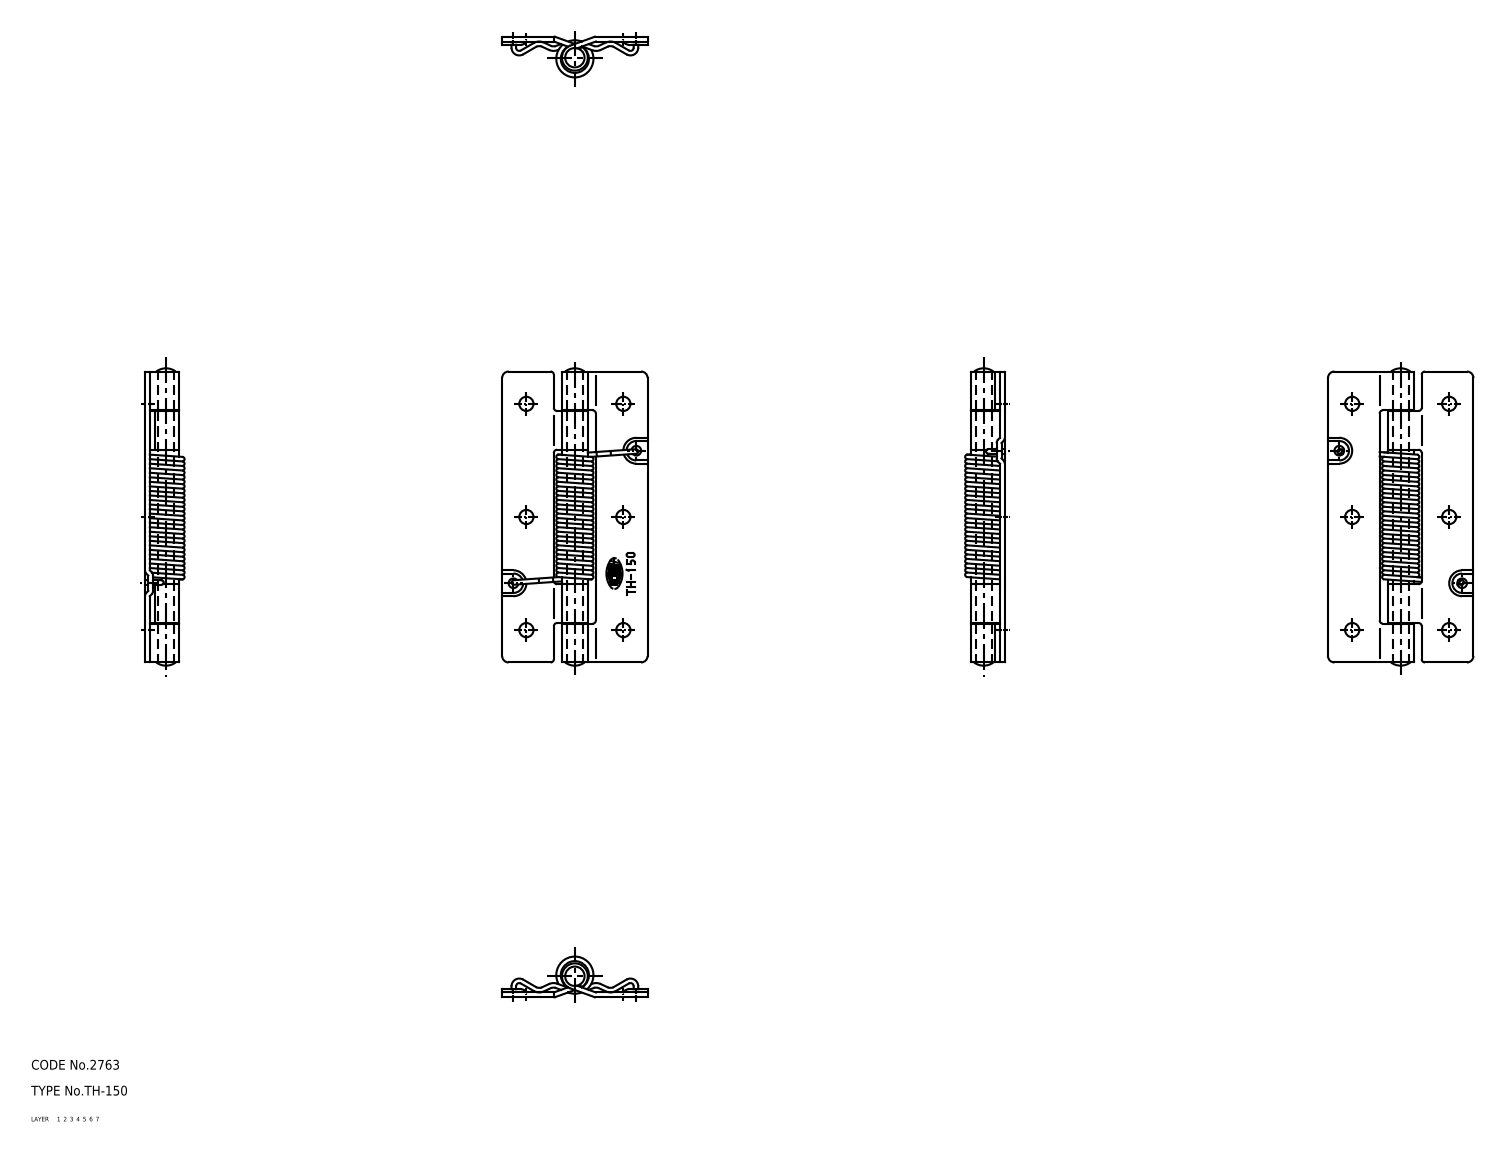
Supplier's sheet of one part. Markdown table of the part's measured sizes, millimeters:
| quantity | value |
| --- | --- |
| part name | 67130467; 67130480; 67130493; 67130506 |
| STEP written by | CADfix (AUTOMOTIVE_DESIGN) |
| units | millimeters |
| bodies | 4 solids, 154 faces (0 planar, 0 cylindrical, 154 other) |
| overall size | 92 × 45 × 12.61 |
| volume | 10 353 mm³ |
| surface area | 14 818 mm² |
